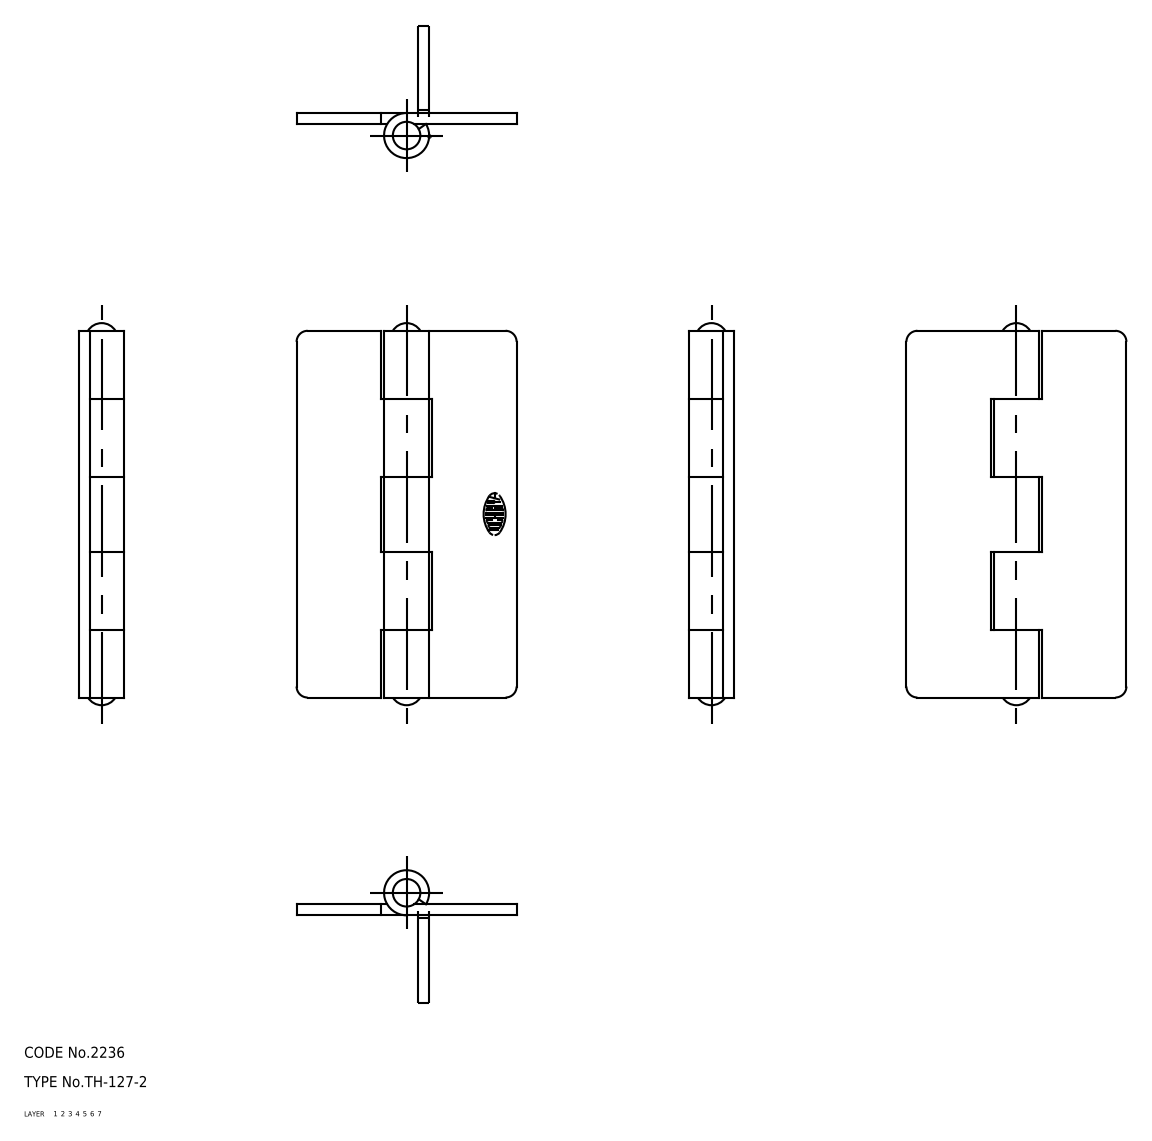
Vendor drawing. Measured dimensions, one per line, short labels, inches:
name: hinge piece_B; hinge piece_A; shaft; TH_127_2_2860_36
written by: CADfix (AUTOMOTIVE_DESIGN)
unit: in
bodies: 3 solids, 48 faces (0 planar, 0 cylindrical, 48 other)
size: 4.102 × 2.362 × 0.484
volume: 1.594 in³; area: 30.84 in²
